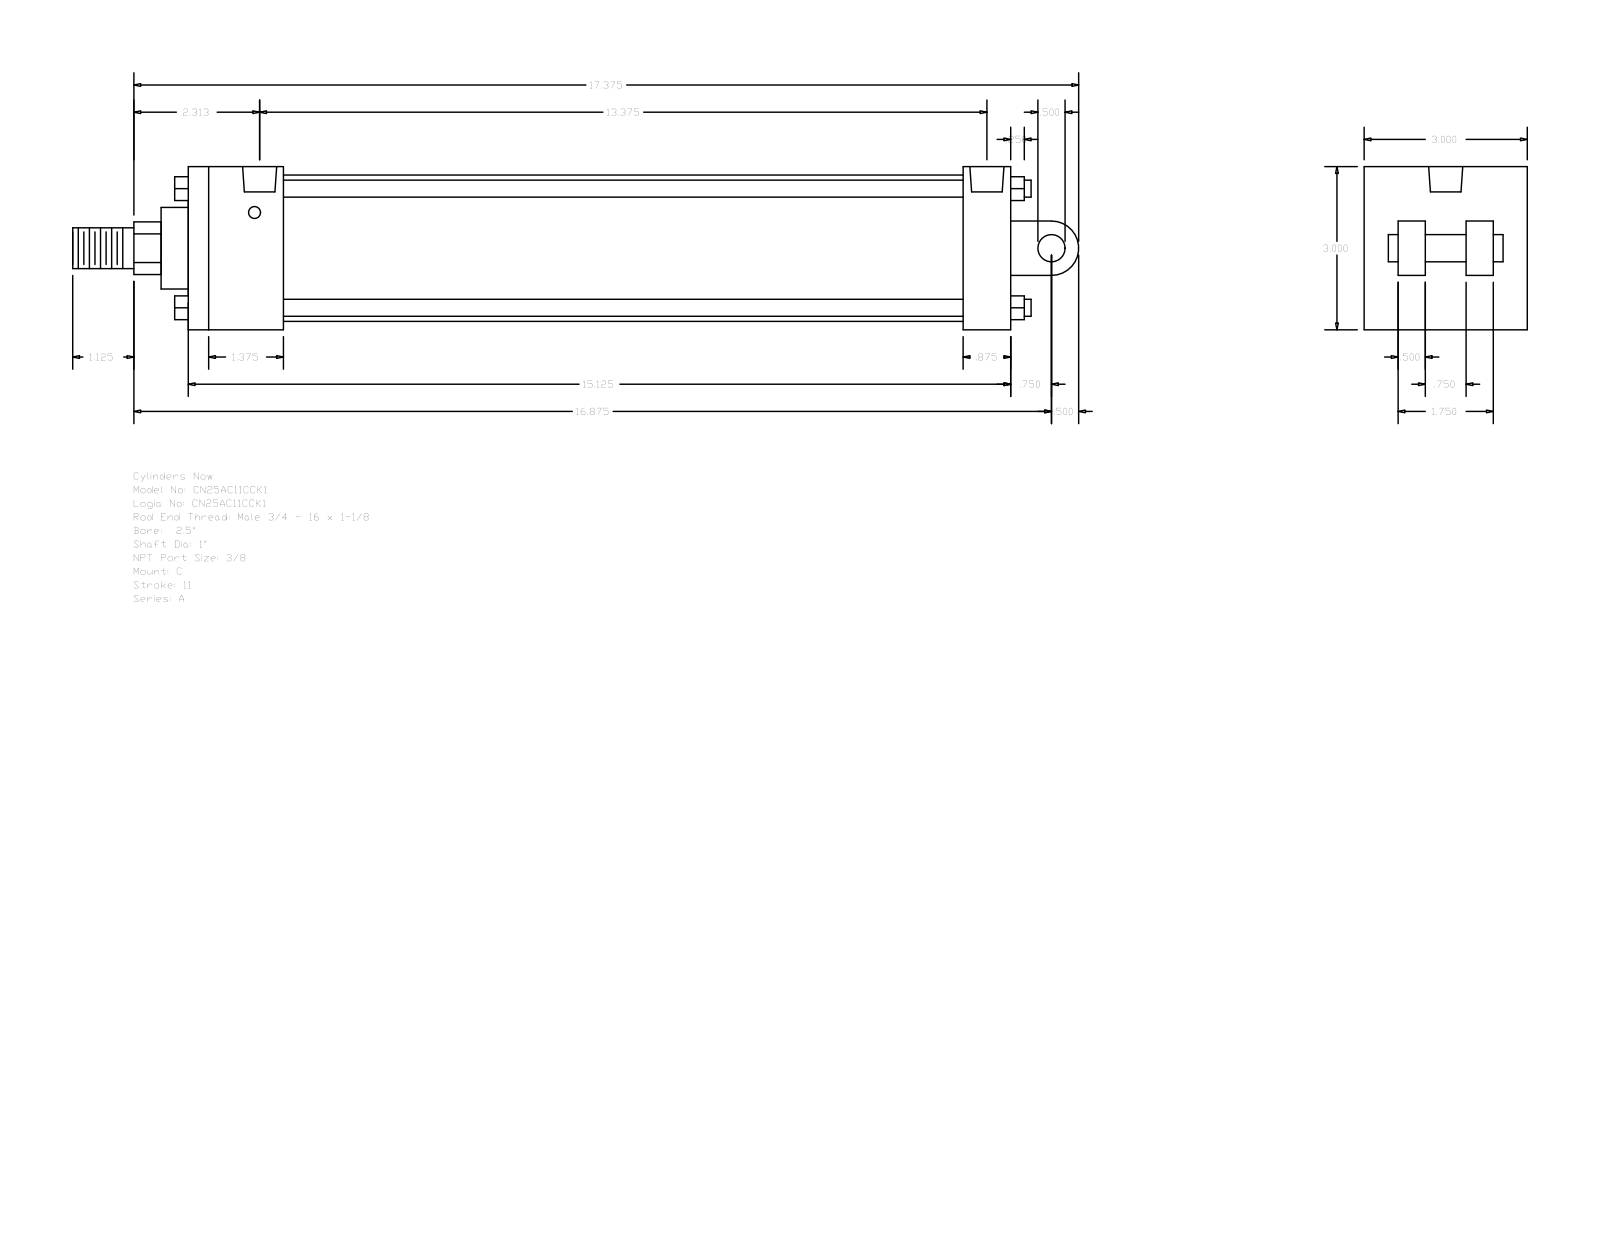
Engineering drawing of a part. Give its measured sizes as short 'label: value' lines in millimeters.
name: A_C__0250_1
written by: GSSL Pune (CONFIG_CONTROL_DESIGN)
unit: mm
bodies: 0 solids, 135 faces (102 planar, 33 cylindrical, 0 other)
size: 469.9 × 76.2 × 76.2
holes: 4× ⌀5.56, 2× ⌀15.93
bosses: 4× ⌀7.94, 1× ⌀68.33, 1× ⌀38.1, 1× ⌀25.4, 1× ⌀19.05, 1× ⌀12.7
rounds: 1× R12.29, 1× R12.7
face distances: 76.2, 384.17, 12.7, 44.45, 361.95, 317.5, 339.72, 22.22, 15.87, 25.4
hole spacings: 2.38, 342.1, 344.48, 339.72
